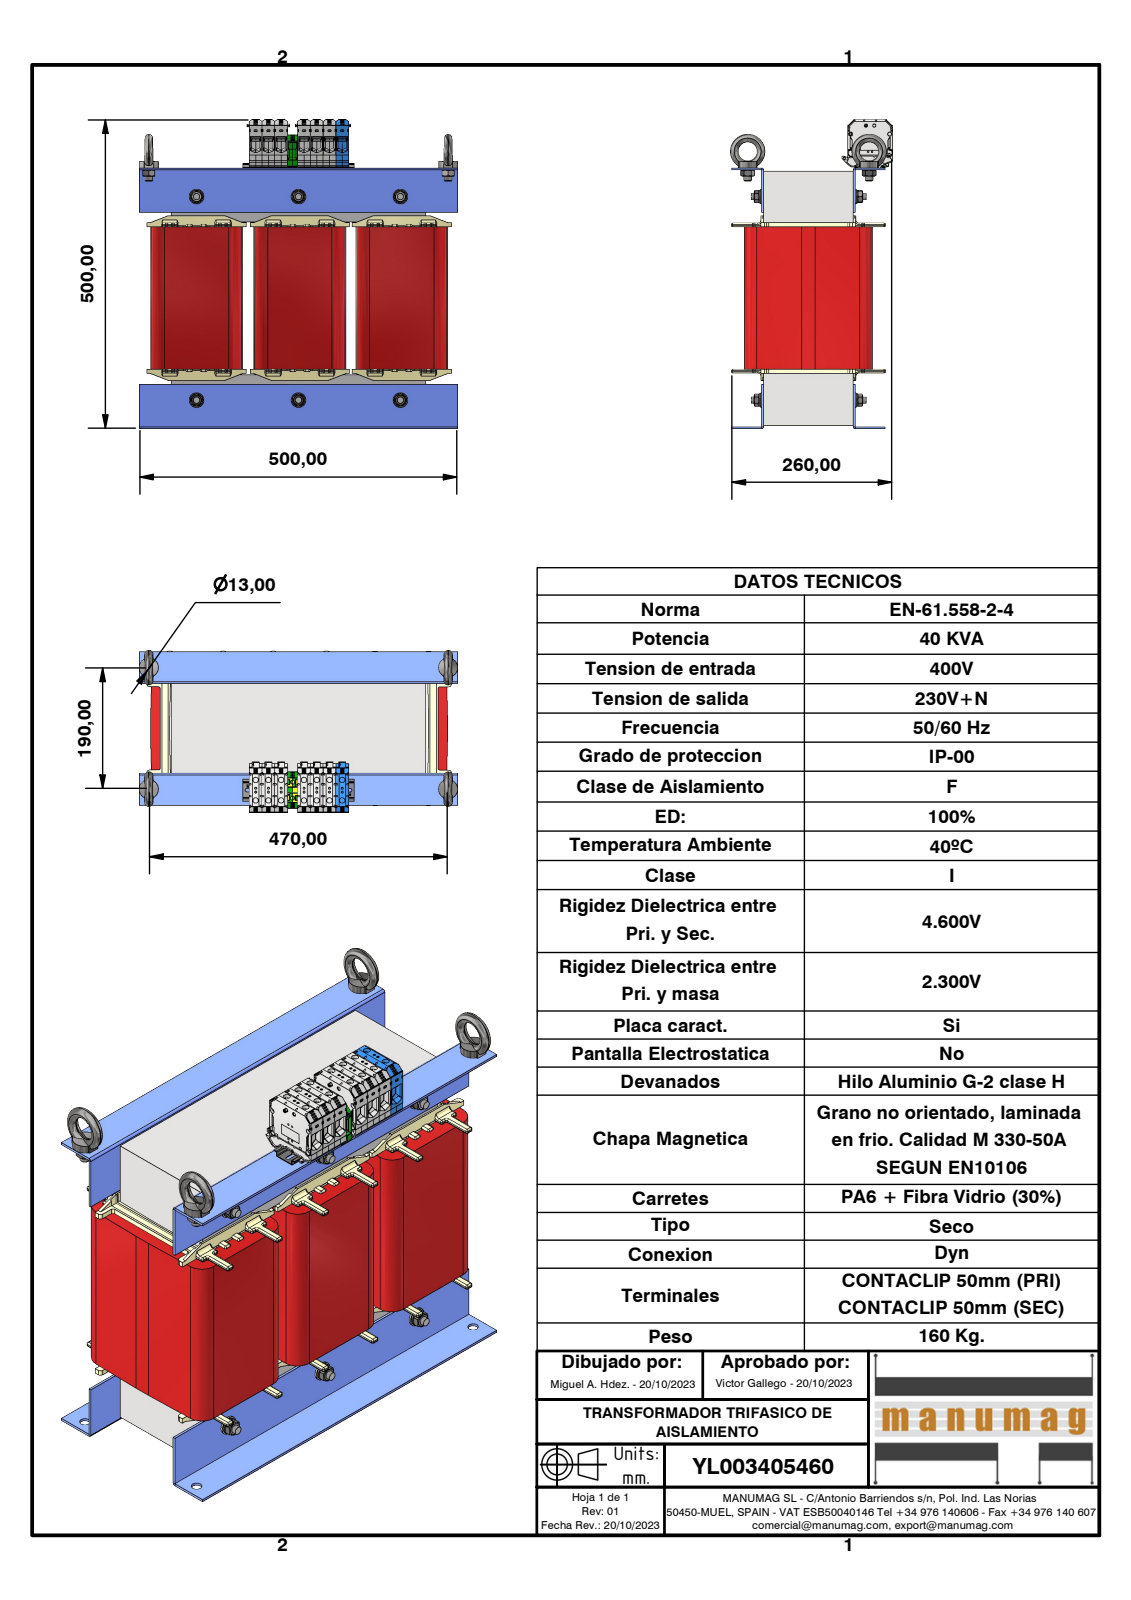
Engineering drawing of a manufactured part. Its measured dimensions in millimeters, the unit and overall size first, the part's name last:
Units: millimetres
Overall size (bounding box): 500 × 486.7 × 253.75
Round holes (diameter × count): ⌀2.75 ×14, ⌀2.95 ×14, ⌀8.5 ×14, ⌀13 ×10, ⌀2.5 ×8, ⌀8.38 ×6, ⌀10 ×6, ⌀10.5 ×6, ⌀15 ×6, ⌀2 ×4, ⌀3.4 ×4, ⌀6.5 ×4
Round bosses / shafts (diameter × count): ⌀23 ×6, ⌀20 ×6, ⌀11.5 ×6, ⌀12 ×4, ⌀10.8 ×4, ⌀54 ×2, ⌀4.6 ×2
Partial cylindrical surfaces — rounded edges, fillets, slot ends (radius × count): R0.3 ×451, R2 ×277, R1 ×266, R0.5 ×68, R0.81 ×33, R1.9 ×32, R0.3 ×26, R0.49 ×24
Main face-to-face distances: 5, 3, 140, 162.39, 2, 29.89, 80, 160, 143, 145.2
Hole centre spacings: 20, 23.85, 27.59, 13, 19, 20.88, 40, 42.06
Volume: 29 430 000 mm³ · Surface area: 3 094 000 mm²
Bodies: 88 solids, 13103 faces (7552 planar, 4281 cylindrical, 1270 other)
Part name (STEP PRODUCT): YL003405460; 3UI240 400 x 400 - 140; UI 240_140_BOBINADO; RC80 NT080 (+8 more)
STEP written by: Autodesk Inventor 2023 (AUTOMOTIVE_DESIGN)
